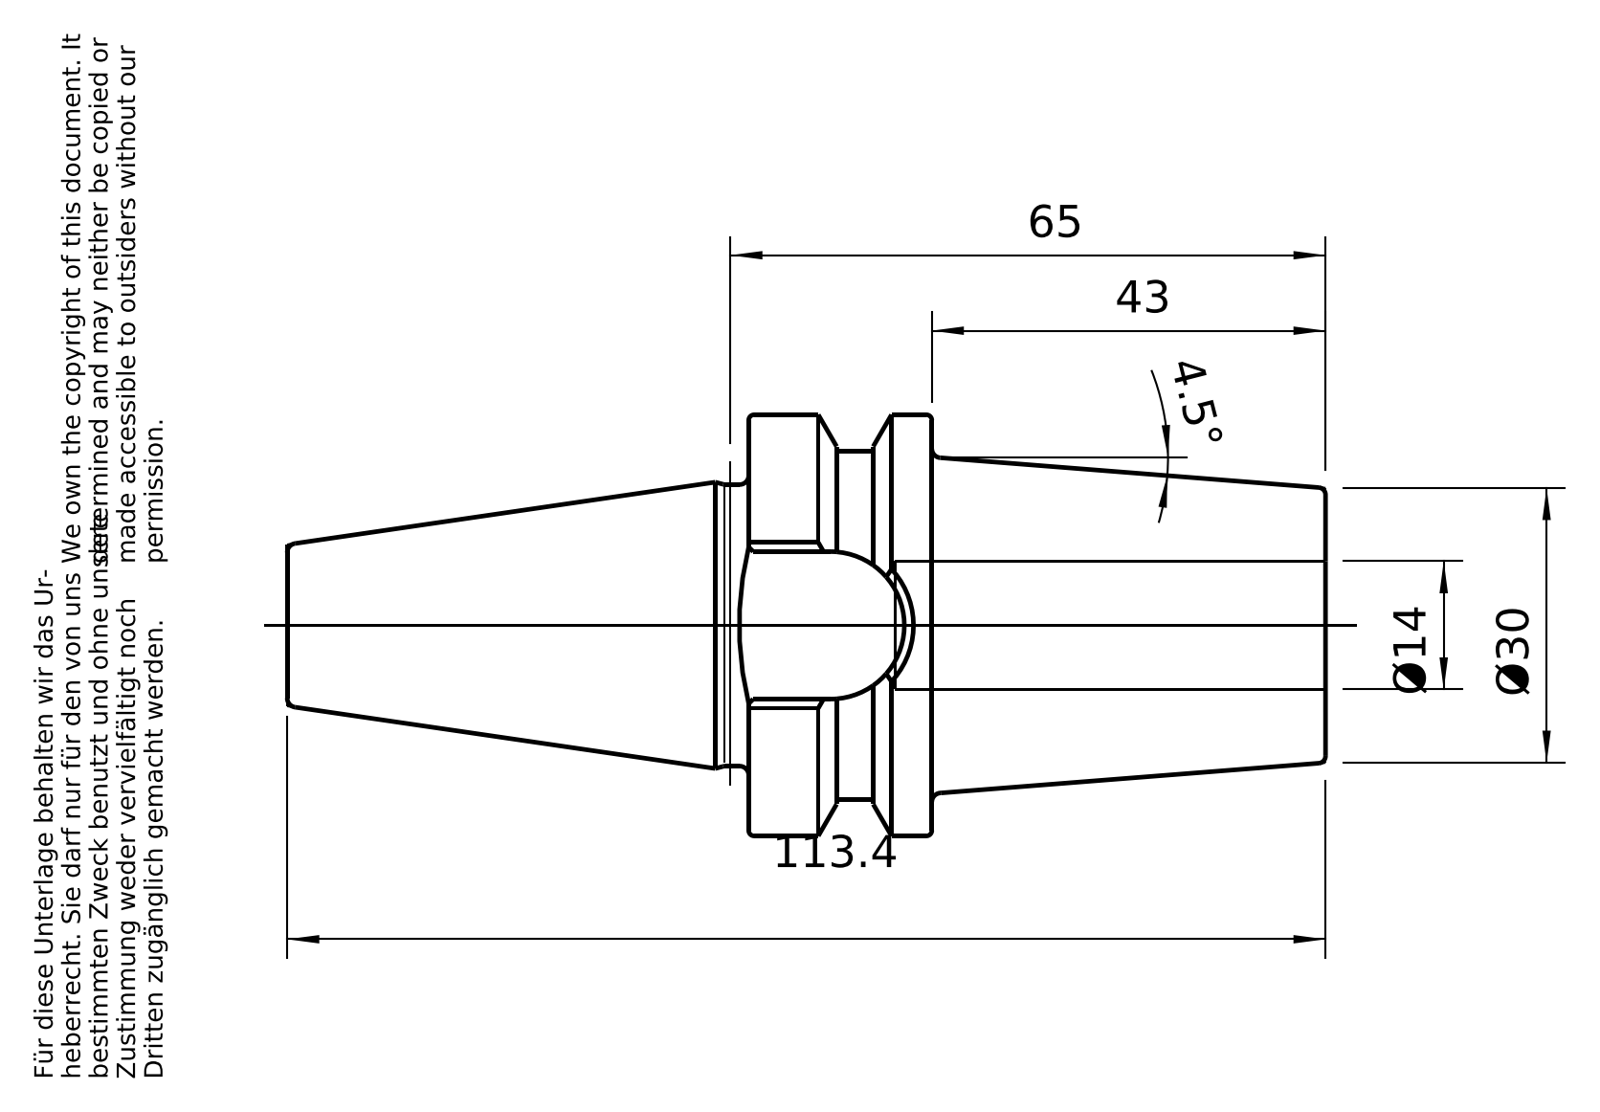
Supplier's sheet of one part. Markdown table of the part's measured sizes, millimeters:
| quantity | value |
| --- | --- |
| part name | 30-645-14 |
| STEP written by | PRO/ENGINEER BY PARAMETRIC TECHNOLOGY CORPORATION, 2010430 (CONFIG_CONTROL_DESIGN) |
| units | millimeters |
| bodies | 1 solid, 94 faces (26 planar, 20 cylindrical, 48 other) |
| overall size | 113.4 × 45.98 × 45.98 |
| volume | 80 059 mm³ |
| surface area | 18 005 mm² |
| round holes (diameter × count) | 10.11 × 1, 12.51 × 1, 13 × 1, 14 × 1 |
| round bosses / shafts (diameter × count) | 45.98 × 1, 30.75 × 1, 12.01 × 1 |
| partial cylindrical surfaces (radius × count) | 8.1 × 1, 18.88 × 1 |
| main face-to-face distances | 63, 20, 43, 32.3, 16, 4, 47, 16.2, 50.4, 66.4 |
